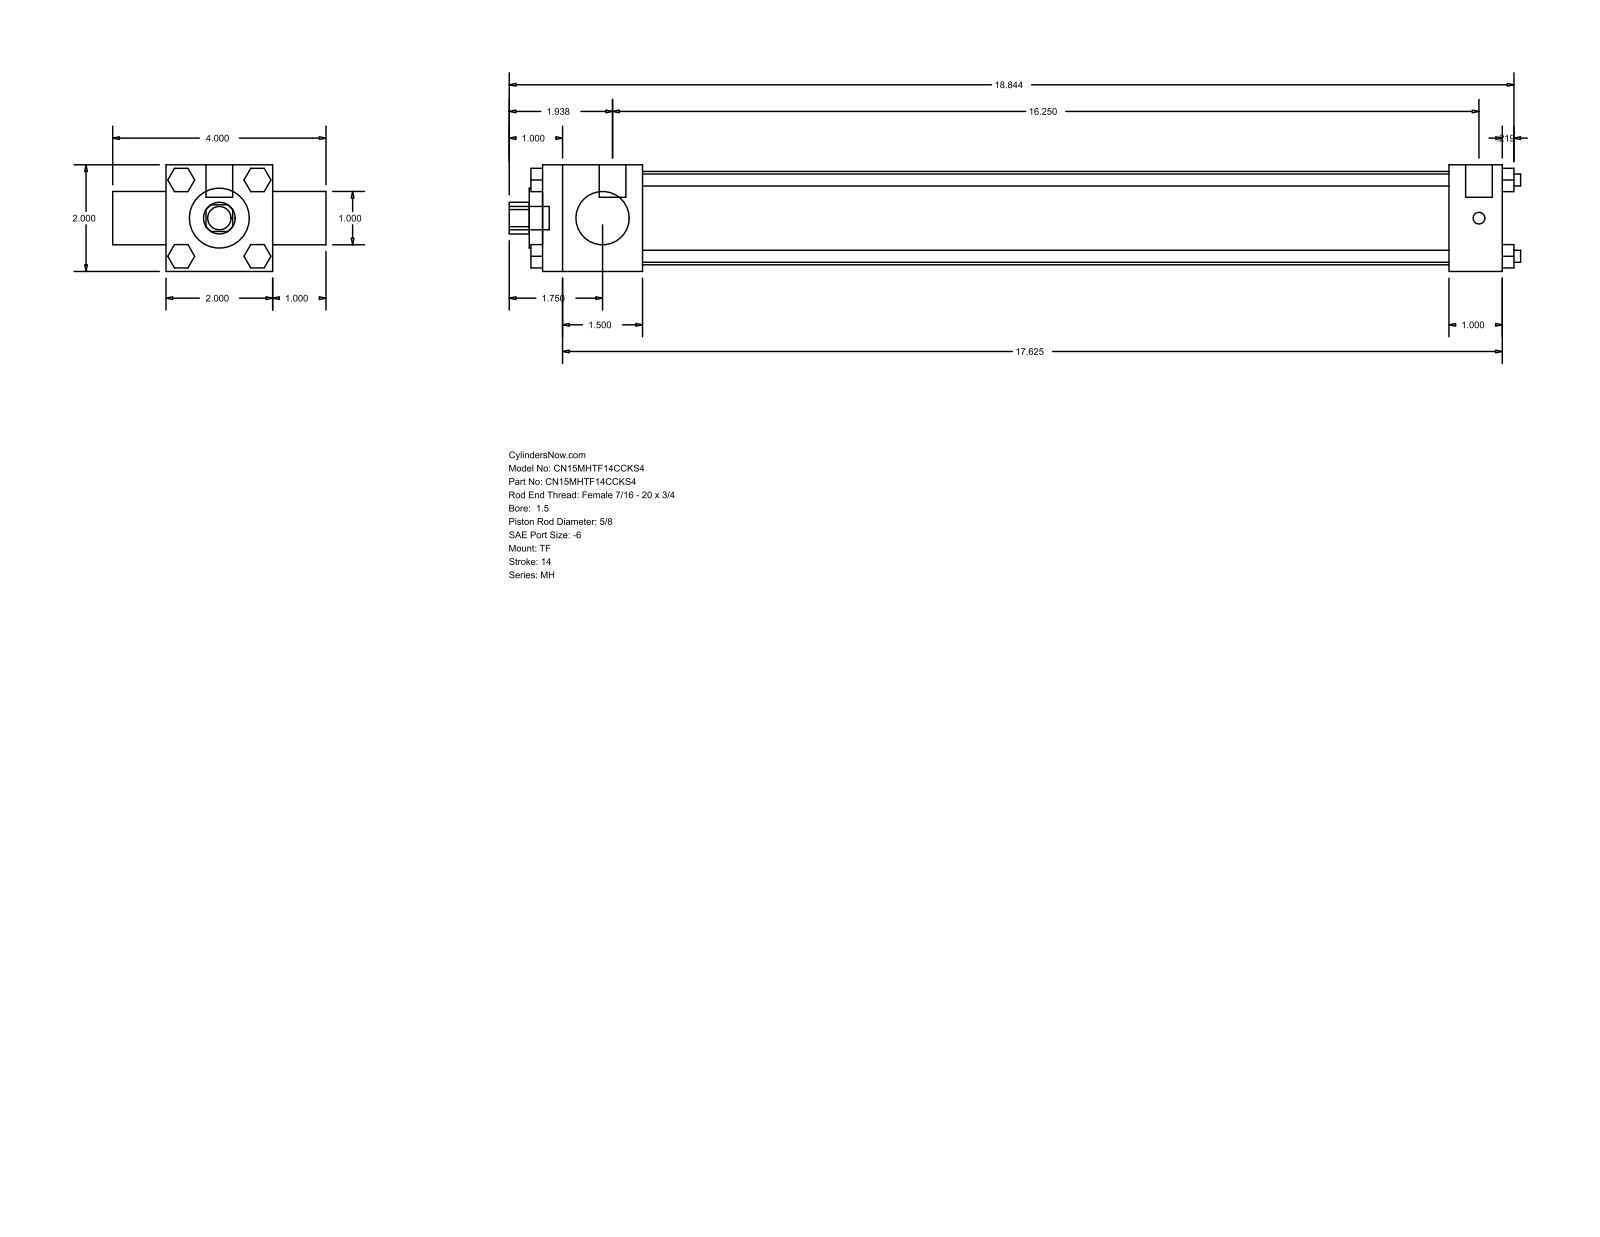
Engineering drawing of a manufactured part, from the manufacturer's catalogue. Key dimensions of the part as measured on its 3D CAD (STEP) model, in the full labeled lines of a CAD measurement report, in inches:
Part name (STEP PRODUCT): MH_TF__0150_0.625
STEP written by: GSSL Pune (CONFIG_CONTROL_DESIGN)
Units: inches
Bodies: 0 solids, 120 faces (92 planar, 28 cylindrical, 0 other)
Overall size (bounding box): 18.969 × 4 × 2
Round holes (diameter × count): ⌀0.625 ×1, ⌀1 ×1, ⌀1.125 ×1, ⌀1.75 ×1
Round bosses / shafts (diameter × count): ⌀0.225 ×4, ⌀0.219 ×3, ⌀0.5 ×2, ⌀0.437 ×1
Partial cylindrical surfaces — rounded edges, fillets, slot ends (radius × count): R0.297 ×1
Main face-to-face distances: 2, 18, 1, 3, 1.875, 16.125, 17, 15.125, 1, 0.219
